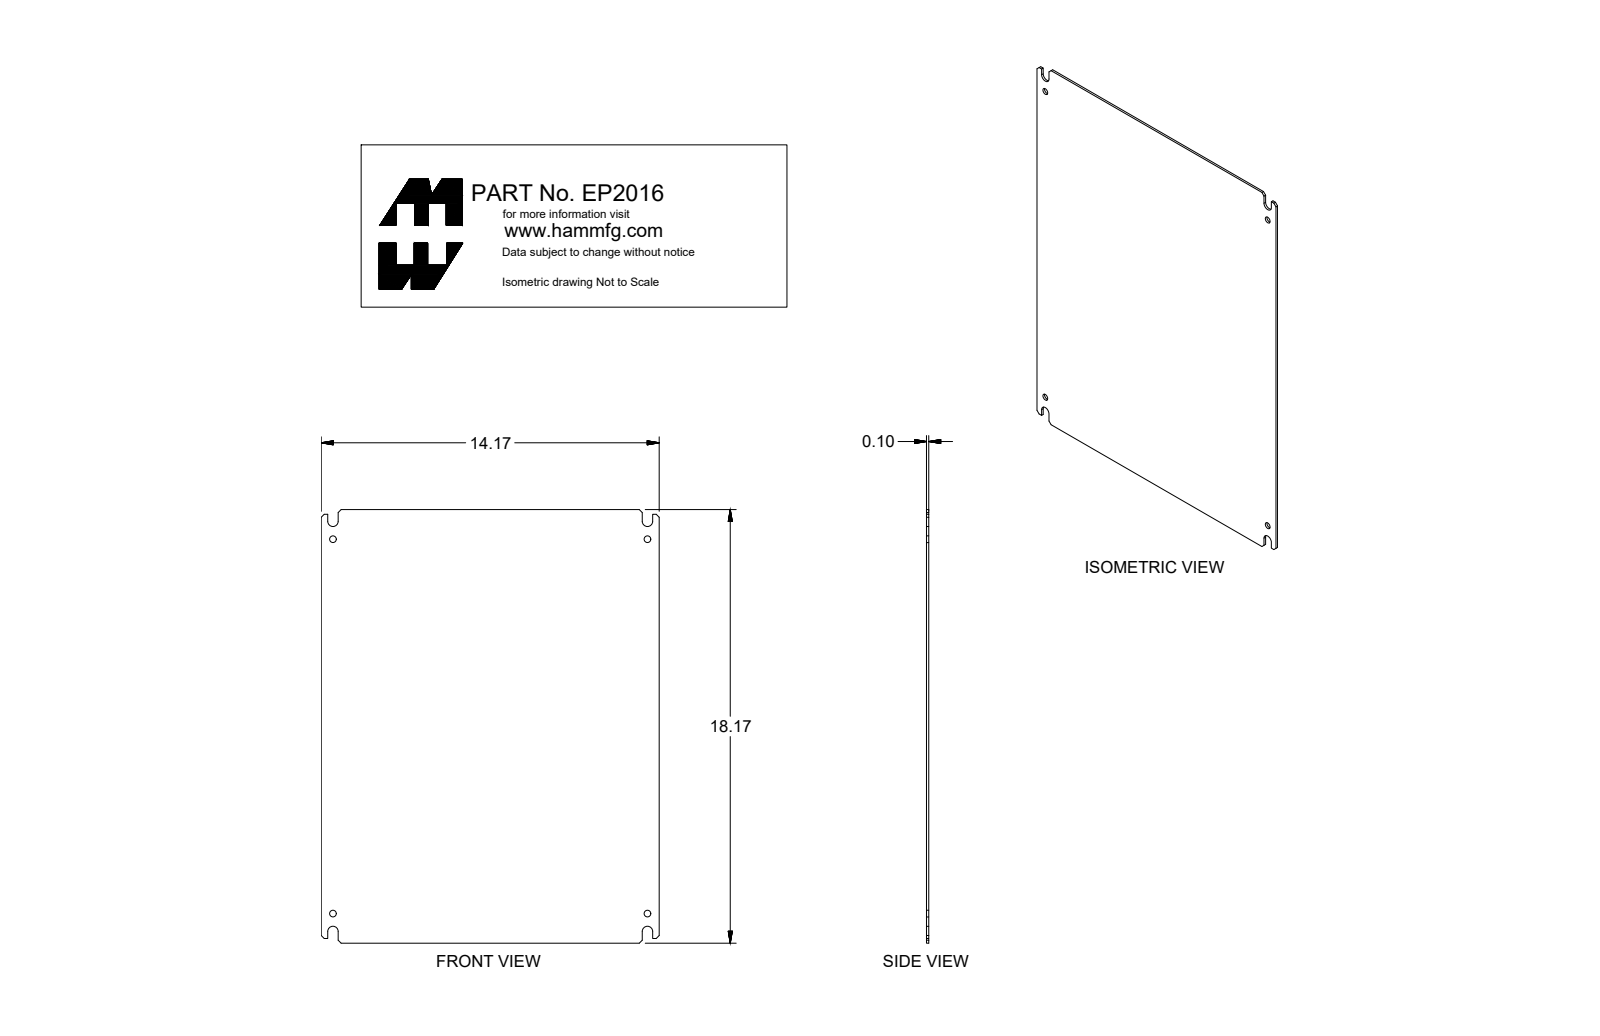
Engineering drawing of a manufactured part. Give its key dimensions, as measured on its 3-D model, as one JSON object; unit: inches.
{"part_name": "EP2016", "step_written_by": "SolidWorks 2018 (AUTOMOTIVE_DESIGN)", "units": "inches", "bodies": {"solids": 1, "faces": 40, "planar": 26, "cylindrical": 14, "other": 0}, "overall_size": [18.17, 14.17, 0.095], "volume_in3": 24.3, "surface_area_in2": 518.3, "round_holes": [[0.281, 4]], "partial_cylinders_radius": [[0.219, 4]], "face_to_face_distances": [0.095, 14.17, 18.17, 0.709, 13.461, 0.272, 13.898, 0.437, 13.188, 12.751], "hole_center_spacings": [13.188, 15.688, 20.495]}
